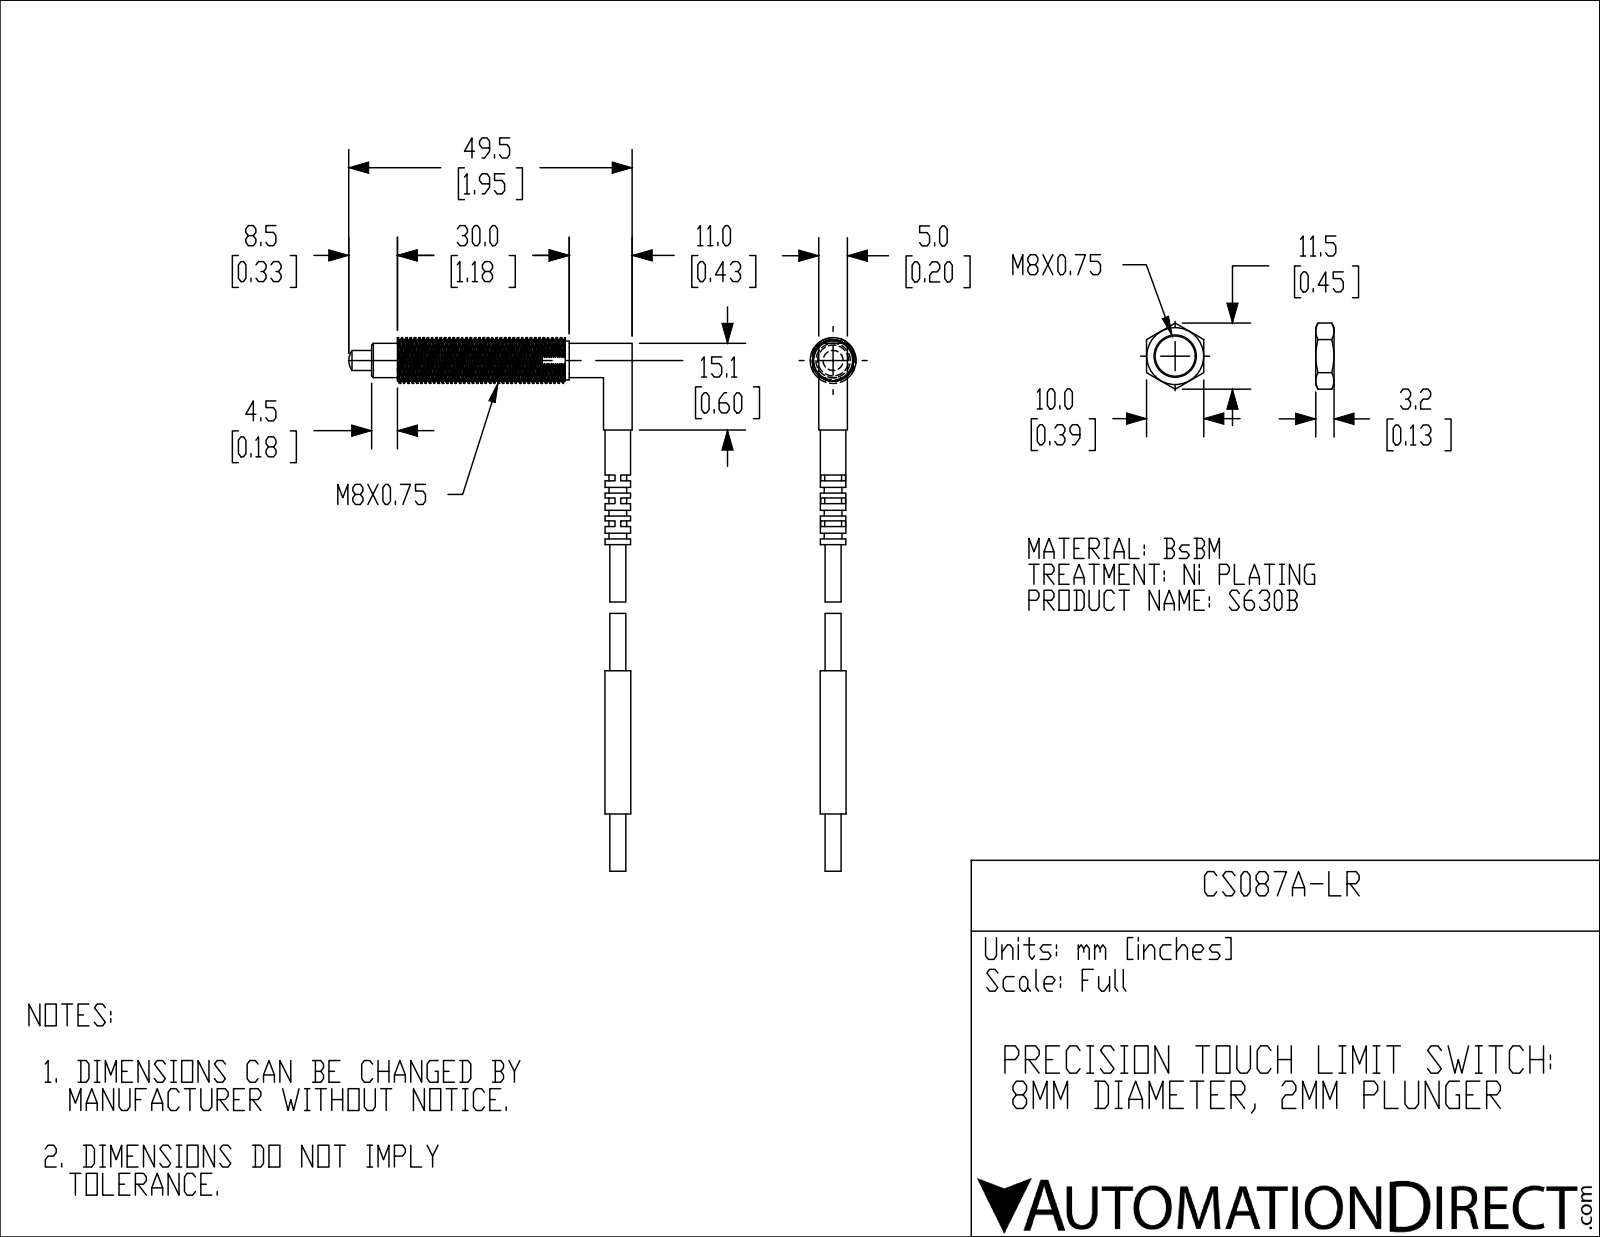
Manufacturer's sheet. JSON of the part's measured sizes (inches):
{"part_name": "CS087A-LR", "step_written_by": "SolidWorks 2018 (AUTOMOTIVE_DESIGN)", "units": "inches", "bodies": {"solids": 2, "faces": 81, "planar": 58, "cylindrical": 21, "other": 2}, "overall_size": [3.668, 1.949, 0.315], "volume_in3": 0.187, "surface_area_in2": 3.716, "round_bosses_or_shafts": [[0.315, 1], [0.268, 1], [0.236, 1], [0.177, 1], [0.175, 1], [0.138, 1], [0.122, 1], [0.11, 1]], "face_to_face_distances": [0.197, 0.039, 0.236, 0.157, 0.085, 0.118, 0.315, 0.276, 0.394, 0.354]}
